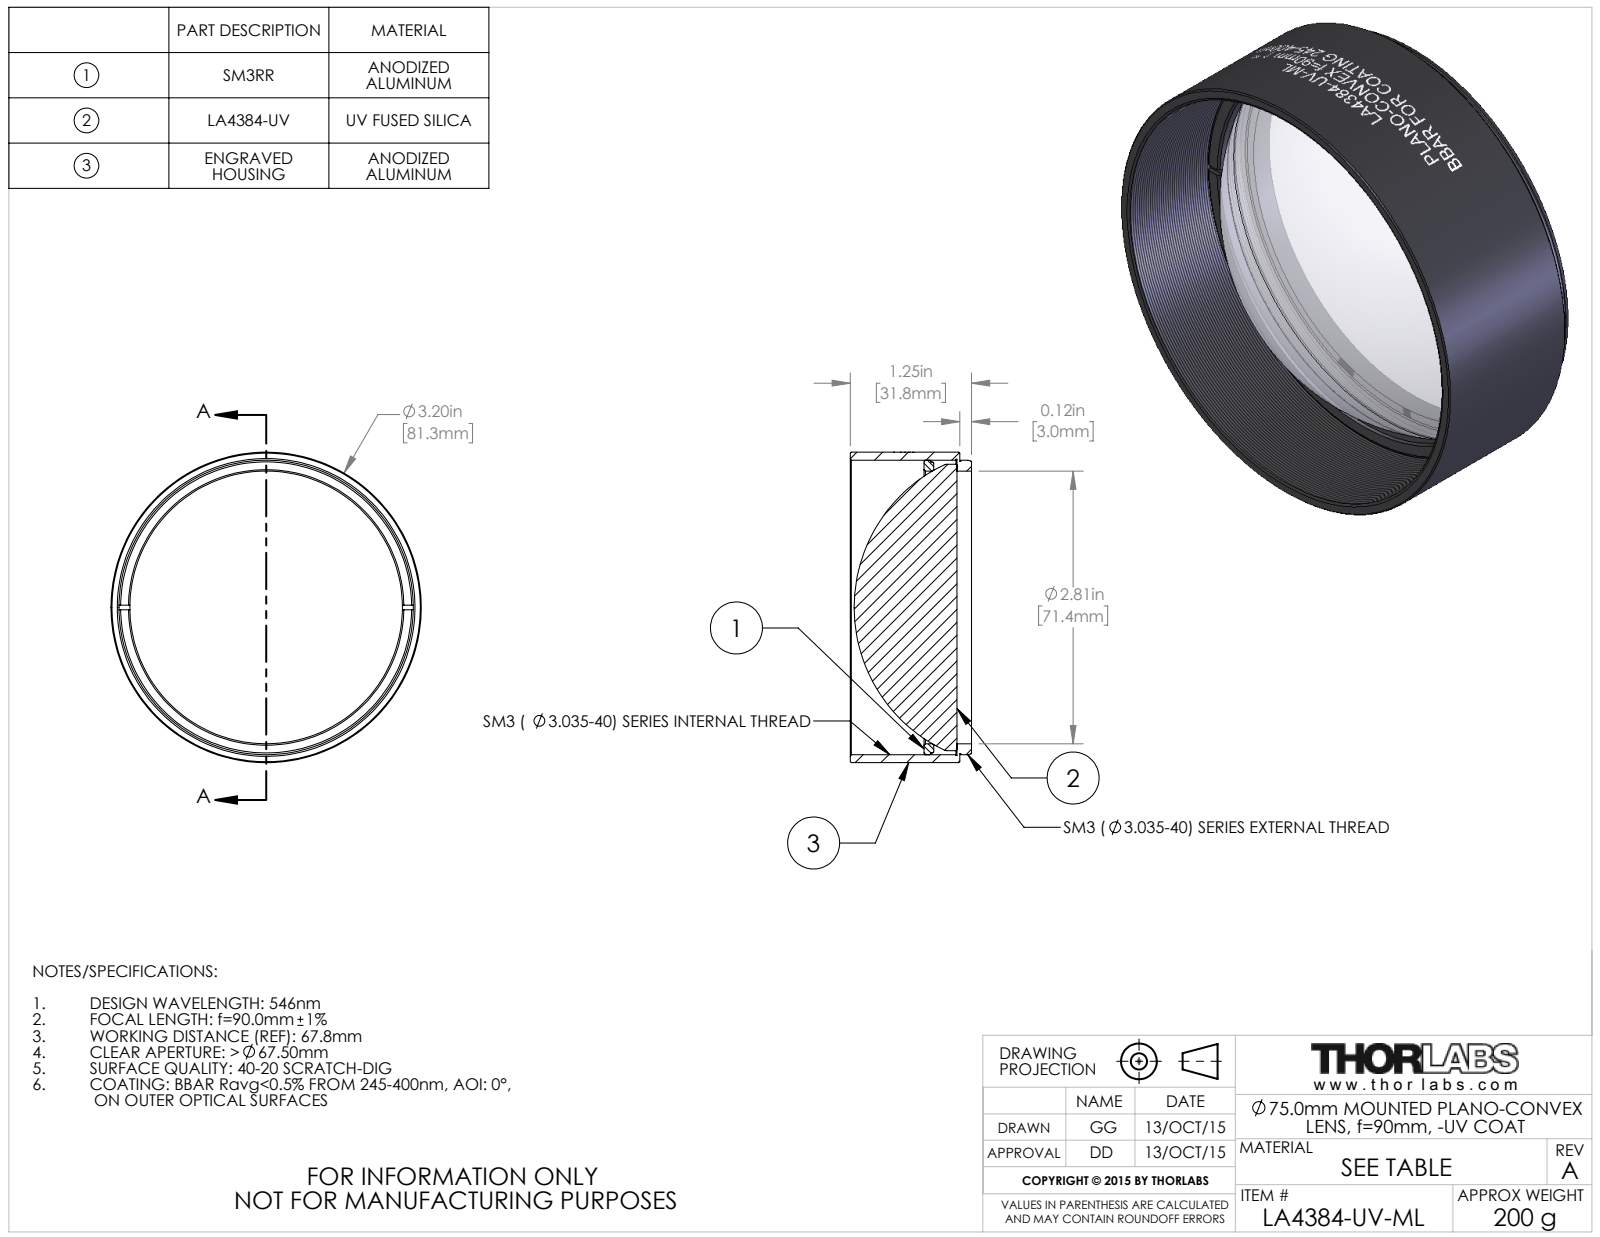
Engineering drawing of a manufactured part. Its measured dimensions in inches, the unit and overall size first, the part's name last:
Units: inches
Overall size (bounding box): 3.2 × 3.2 × 1.25
Round holes (diameter × count): ⌀2.81 ×1, ⌀3.055 ×1
Round bosses / shafts (diameter × count): ⌀3.2 ×1, ⌀3.035 ×1, ⌀3.015 ×1, ⌀2.998 ×1, ⌀2.953 ×1
Main face-to-face distances: 0.15, 0.12, 0.03, 0.489, 0.369, 0.339, 0.389, 0.269, 0.239, 0.1
Volume: 5.621 in³ · Surface area: 49.16 in²
Bodies: 3 solids, 161 faces (17 planar, 116 cylindrical, 28 other)
Part name (STEP PRODUCT): TTN039280-E0W
STEP written by: SolidWorks 2016 (CONFIG_CONTROL_DESIGN)
